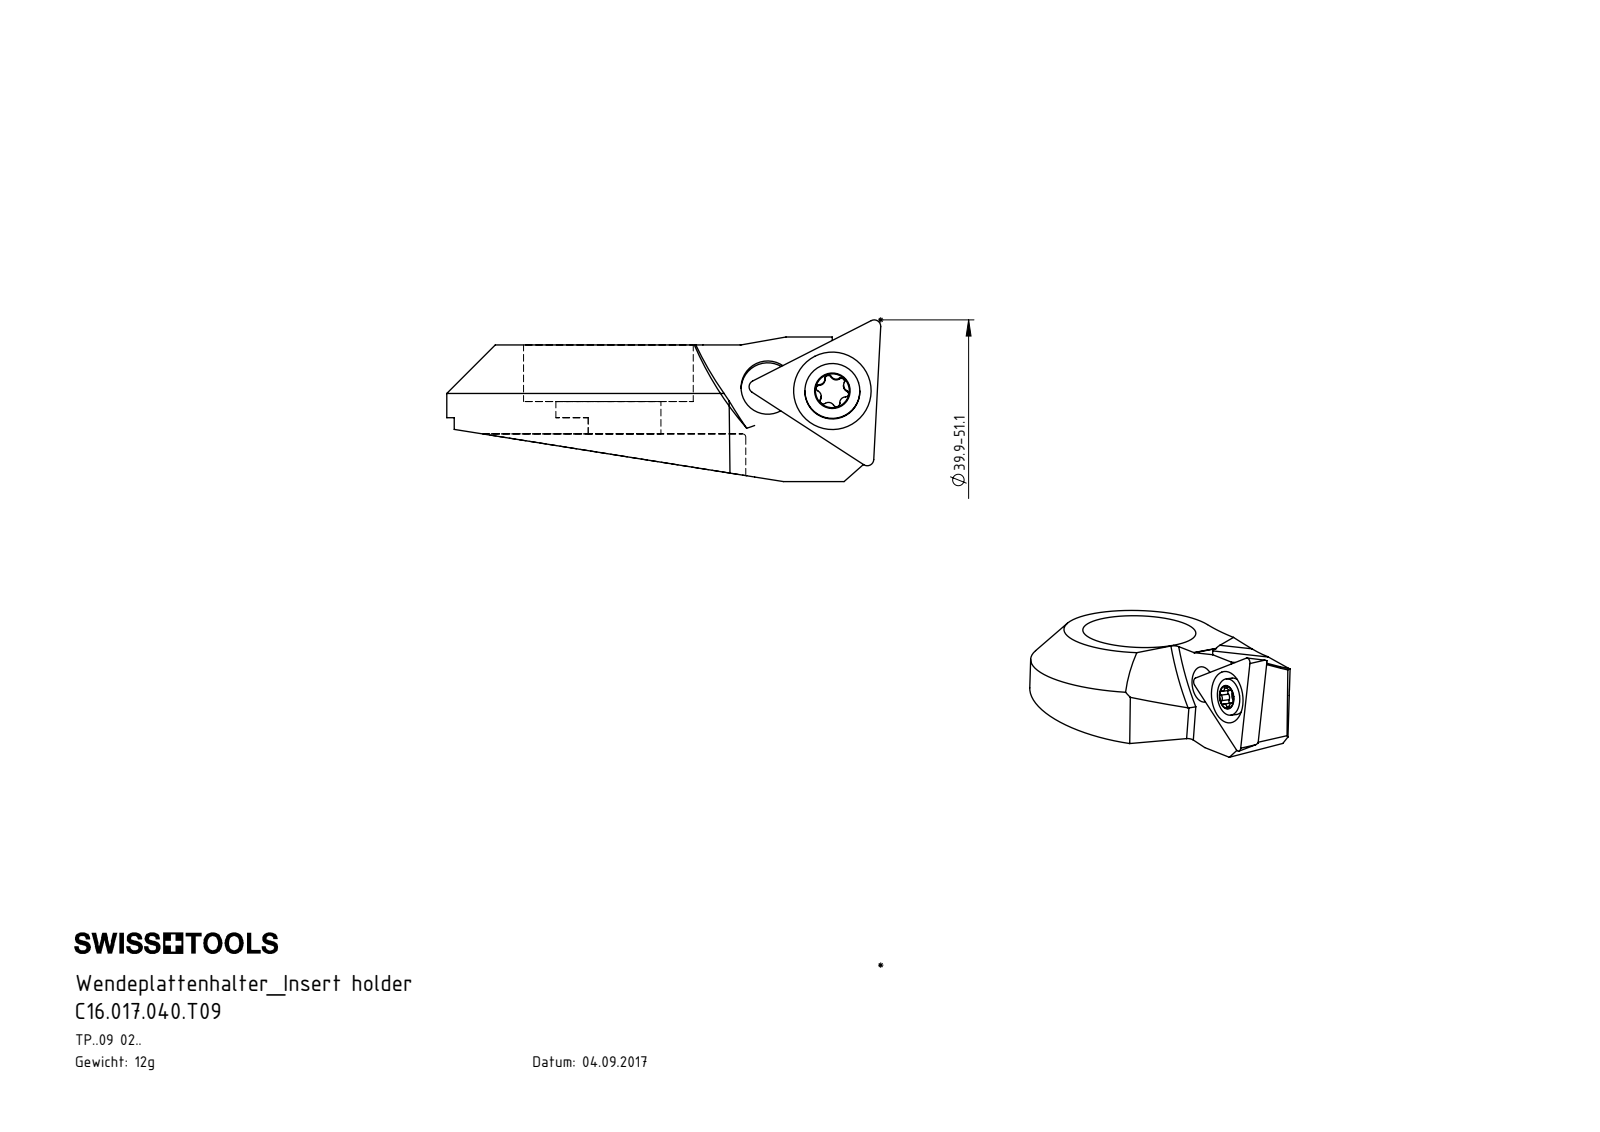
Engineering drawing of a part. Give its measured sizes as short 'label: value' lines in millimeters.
name: C16.017.040.T09; F32-WTH.001.007_A_fertigbearbeitet; TPGH090204; WCA-ER2.001.006_A
written by: SolidWorks 2017 (AUTOMOTIVE_DESIGN)
unit: mm
bodies: 3 solids, 102 faces (33 planar, 41 cylindrical, 28 other)
size: 26.85 × 20 × 10
volume: 1 534 mm³; area: 1 539 mm²
holes: 1× ⌀2.05, 1× ⌀2.8, 1× ⌀6.5, 1× ⌀10.5
bosses: 1× ⌀3.4, 1× ⌀2.5
rounds: 6× R0.21, 5× R0.36, 2× R0.5, 1× R0.36, 1× R1.65, 1× R3, 1× R5, 1× R8.5
face distances: 1, 5.5, 3.5, 2, 4.5, 2.17, 8.45, 4.95, 3.95, 2.95
